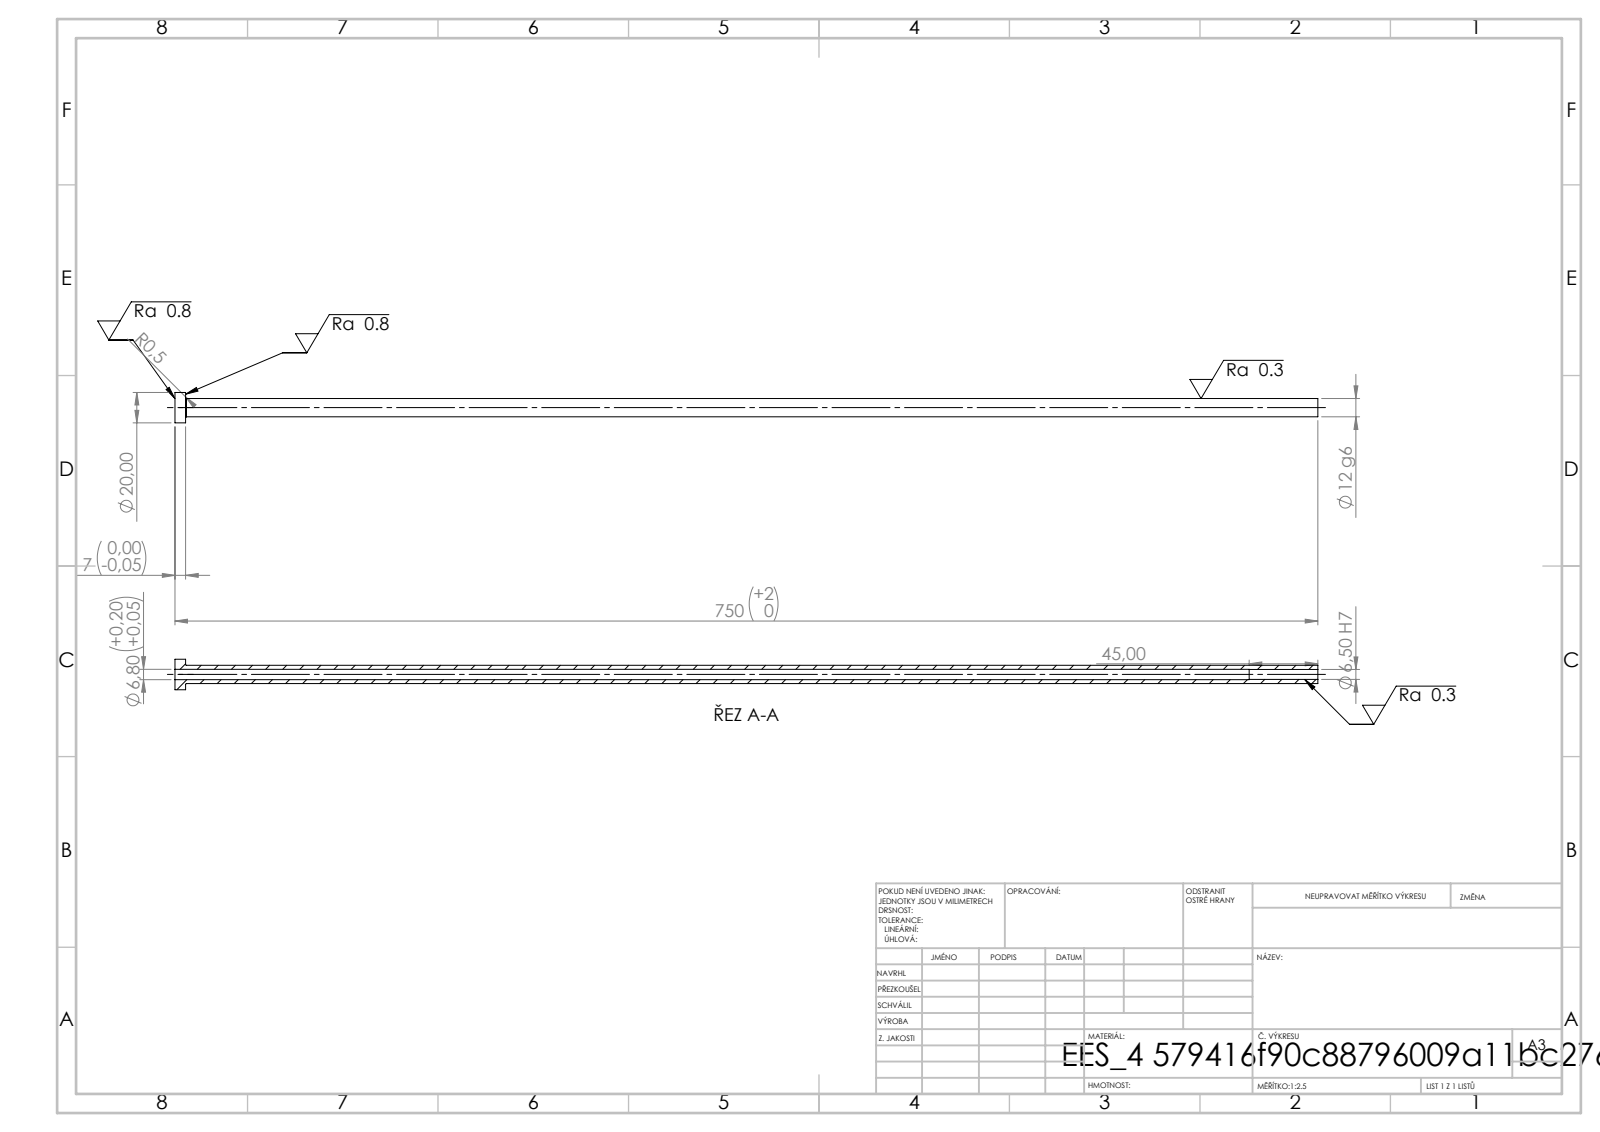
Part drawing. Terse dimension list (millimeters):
written by: SolidWorks 2019 (CONFIG_CONTROL_DESIGN)
unit: mm
bodies: 1 solid, 14 faces (4 planar, 8 cylindrical, 2 other)
size: 750 × 20 × 20
volume: 59 136 mm³; area: 44 984 mm²
holes: 1× ⌀6.5, 1× ⌀6.8
bosses: 1× ⌀20, 1× ⌀12
face distances: 7, 750, 743, 705, 698, 45
